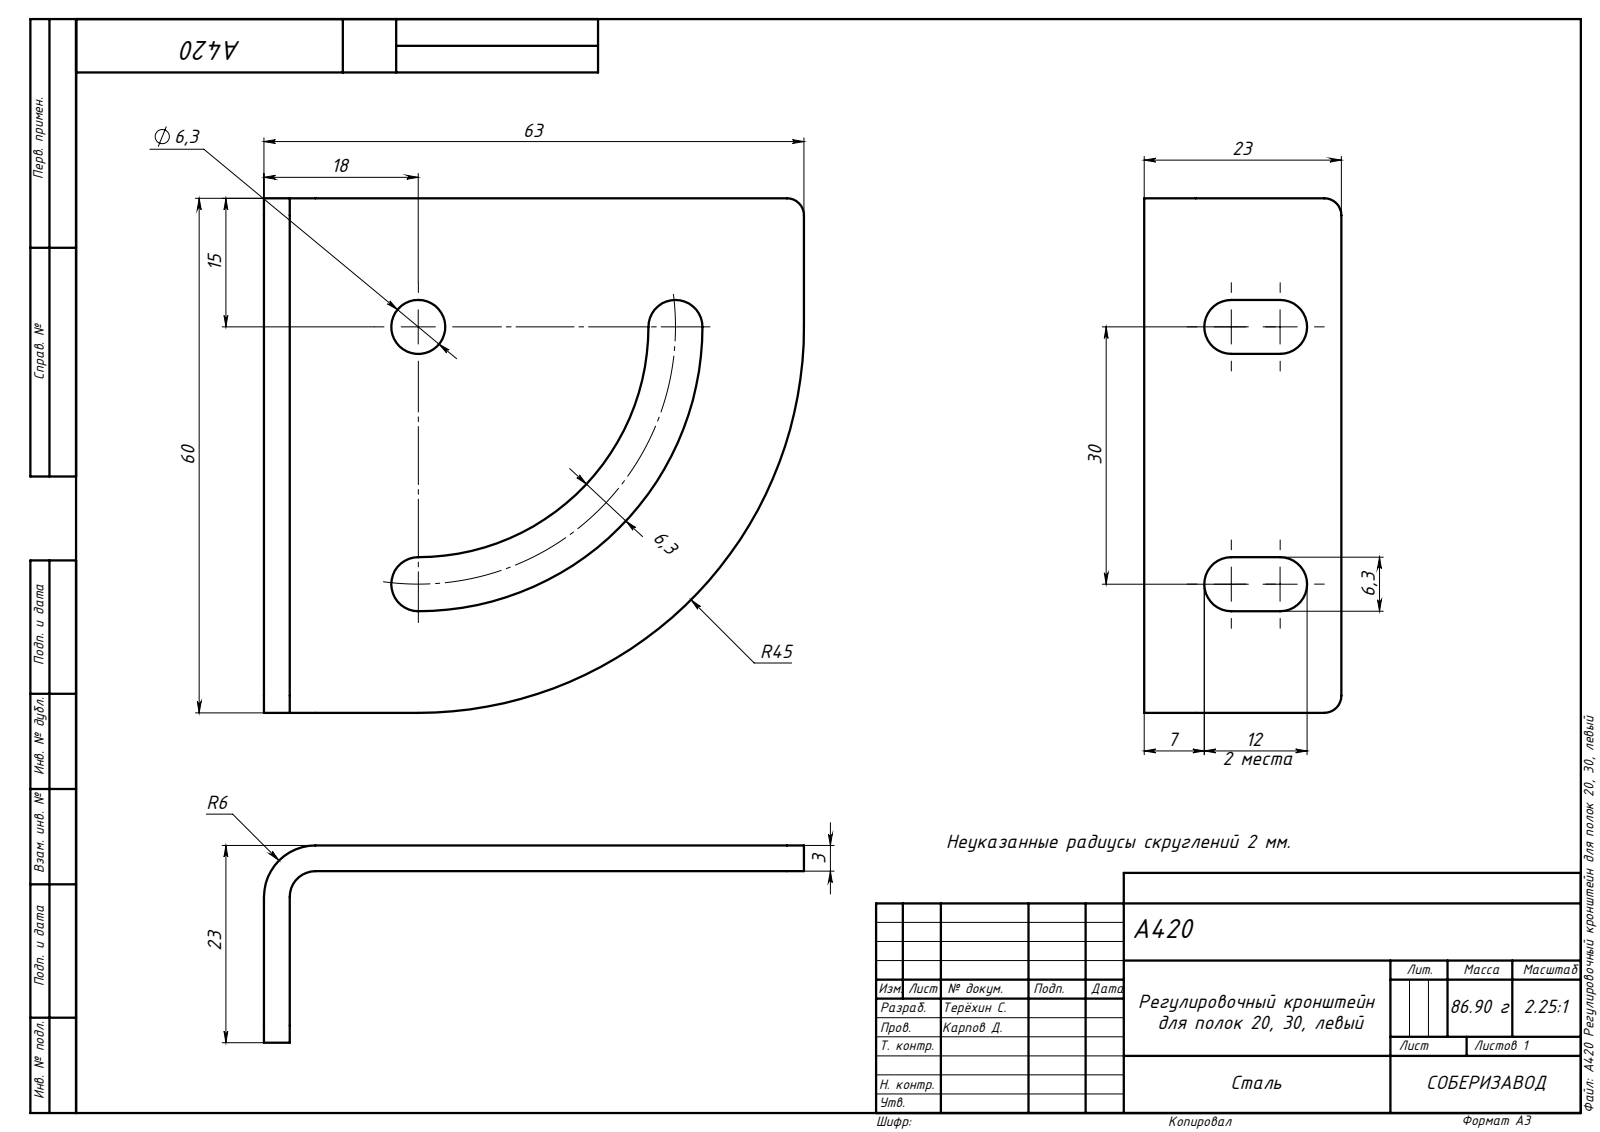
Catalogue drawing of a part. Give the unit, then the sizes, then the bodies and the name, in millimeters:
Units: millimetres
Overall size (bounding box): 63 × 60 × 23
Round holes (diameter × count): ⌀6.3 ×1
Partial cylindrical surfaces — rounded edges, fillets, slot ends (radius × count): R3.15 ×6, R2 ×3, R3 ×1, R6 ×1, R26.85 ×1, R33.15 ×1, R45 ×1
Main face-to-face distances: 3, 20, 23, 60, 63, 18.15, 41.85, 11.85, 48.15, 6.3
Volume: 11 801 mm³ · Surface area: 9 237 mm²
Bodies: 1 solid, 34 faces (16 planar, 18 cylindrical, 0 other)
Part name (STEP PRODUCT): A420 Регулировочный кронштейн для полок 20, 30, левый
STEP written by: SolidWorks 2020 (AUTOMOTIVE_DESIGN)
